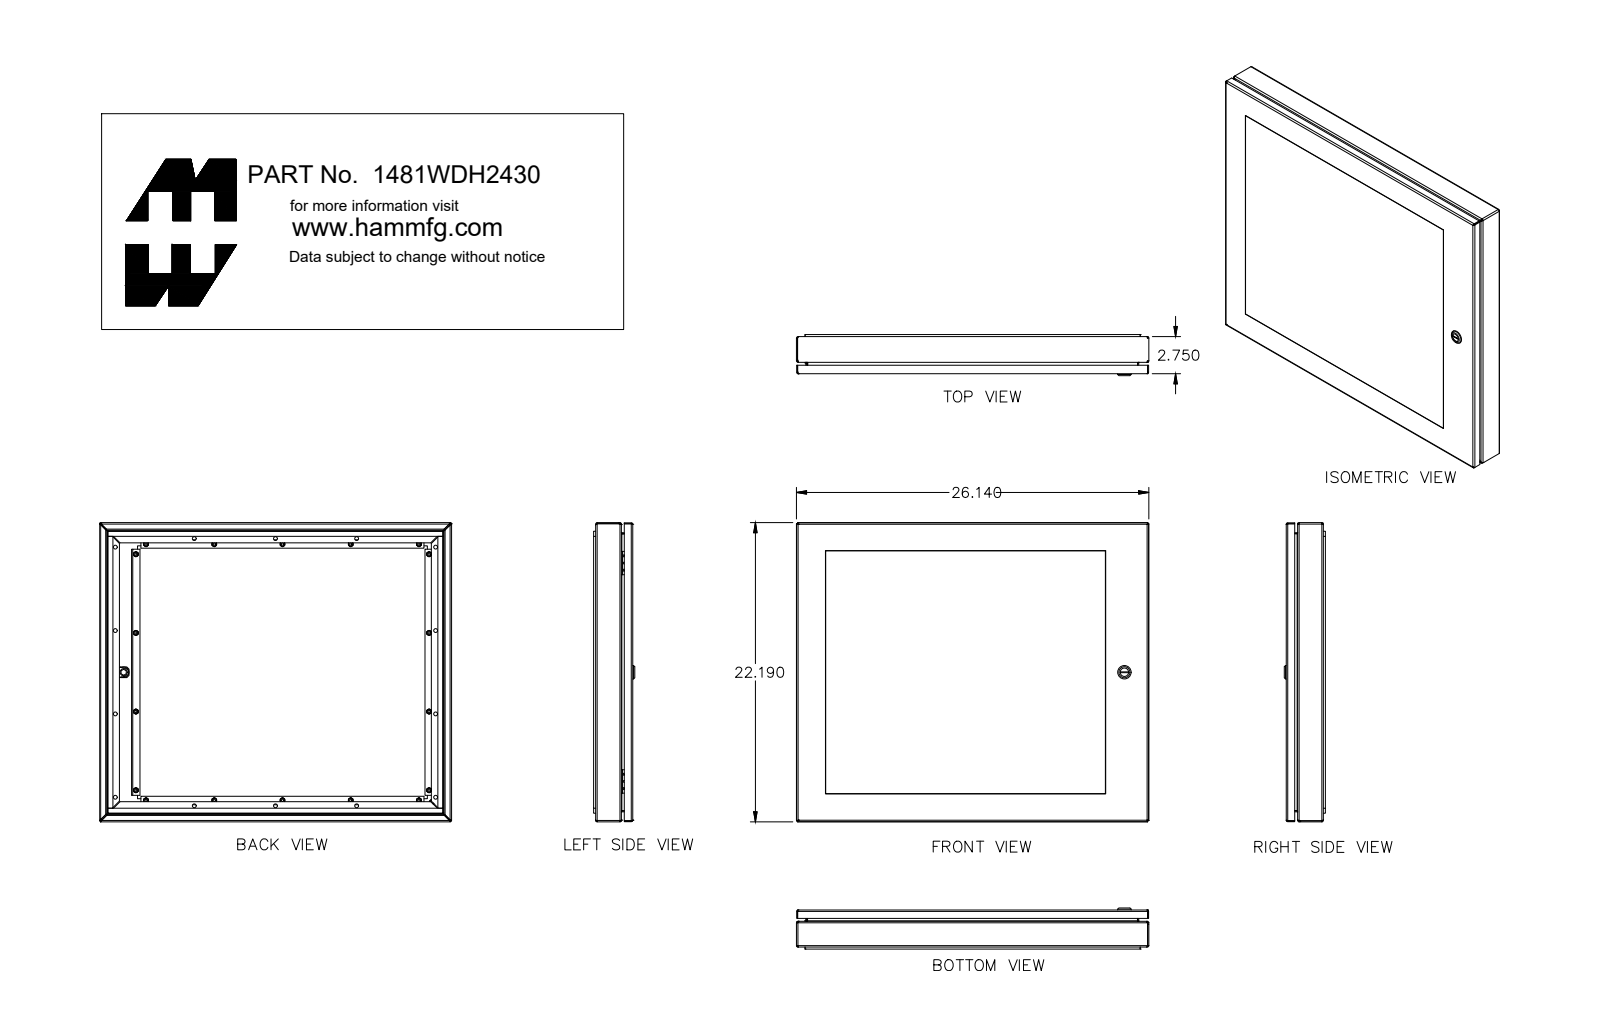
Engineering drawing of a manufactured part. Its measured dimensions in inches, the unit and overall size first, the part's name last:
Units: inches
Overall size (bounding box): 26.14 × 22.19 × 2.91
Round holes (diameter × count): ⌀0.13 ×18, ⌀0.281 ×14, ⌀0.136 ×2, ⌀0.232 ×1, ⌀0.24 ×1, ⌀0.242 ×1, ⌀0.625 ×1, ⌀0.785 ×1
Round bosses / shafts (diameter × count): ⌀0.368 ×18, ⌀0.226 ×18, ⌀0.164 ×18, ⌀1.1 ×1, ⌀0.525 ×1, ⌀0.455 ×1, ⌀0.398 ×1, ⌀0.356 ×1
Partial cylindrical surfaces — rounded edges, fillets, slot ends (radius × count): R0.101 ×36, R0.036 ×28, R0.108 ×28, R0.016 ×4, R0.088 ×4, R0.125 ×2, R0.021 ×1, R0.029 ×1
Main face-to-face distances: 0.072, 0.25, 0.178, 2.578, 2.328, 0.842, 1.736, 0.592, 22.118, 2.65
Hole centre spacings: 19.663, 5.063, 24.555, 22.519, 5.687, 5.833, 6.182, 6.23
Volume: 151.9 in³ · Surface area: 2 412 in²
Bodies: 57 solids, 1292 faces (683 planar, 375 cylindrical, 234 other)
Part name (STEP PRODUCT): 1481WDH2430_Default
STEP written by: SolidWorks 2019 (CONFIG_CONTROL_DESIGN)
